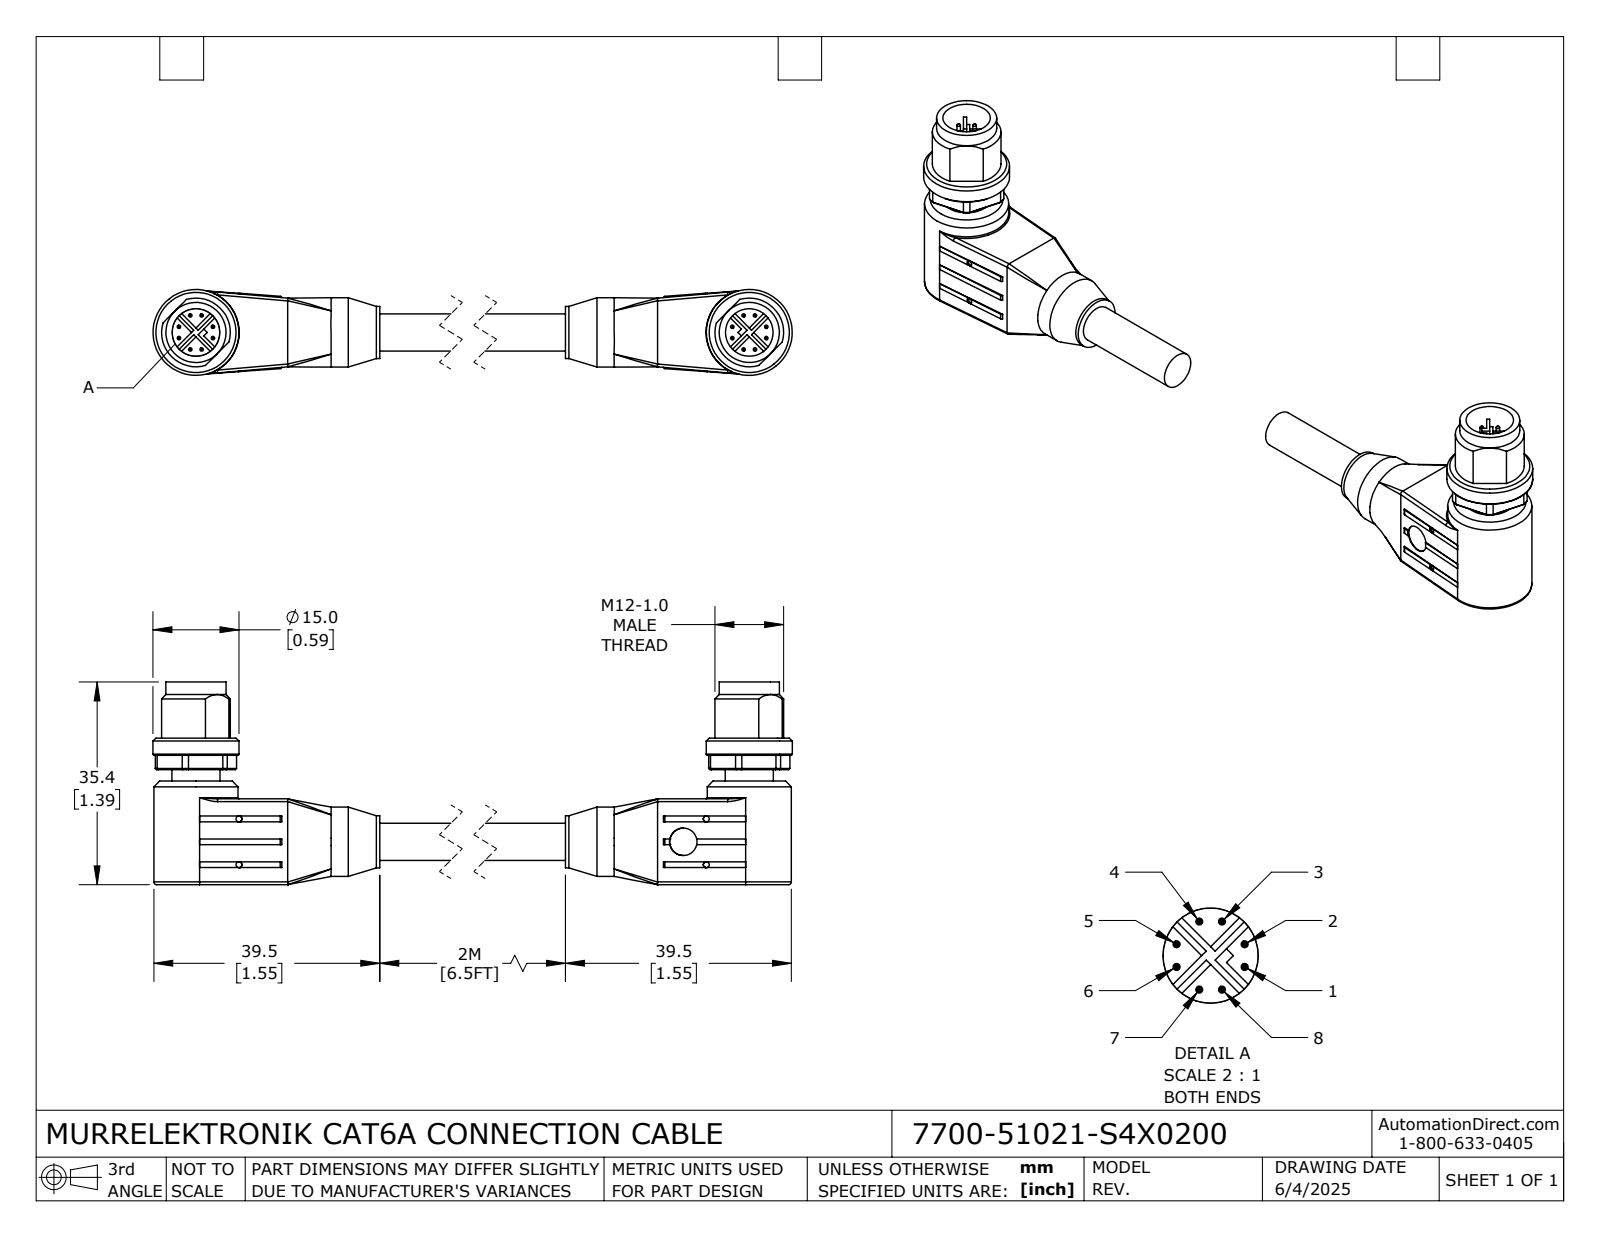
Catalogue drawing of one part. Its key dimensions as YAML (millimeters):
part_name: "7700-51021-S4X0200_MALE; 7700-51021-S4X0200"
step_written_by: "SolidWorks 2024 (CONFIG_CONTROL_DESIGN)"
units: millimeters
bodies: {solids: 2, faces: 424, planar: 196, cylindrical: 134, other: 94}
overall_size: [144.2, 35.4, 15]
volume: 18415
surface_area: 8016
round_holes:
  - {diameter: 1.05, count: 8}
  - {diameter: 4.8, count: 2}
  - {diameter: 8.3, count: 2}
round_bosses_or_shafts:
  - {diameter: 0.6, count: 16}
  - {diameter: 15, count: 2}
  - {diameter: 14.7, count: 2}
  - {diameter: 10.5, count: 2}
  - {diameter: 8.4, count: 2}
  - {diameter: 12.1, count: 1}
  - {diameter: 9.1, count: 1}
  - {diameter: 6.5, count: 1}
partial_cylinders:
  - {radius: 0.5, count: 8}
  - {radius: 0.3, count: 4}
  - {radius: 6, count: 2}
  - {radius: 7.2, count: 2}
face_to_face_distances: [3.59, 15, 91.34, 20.1, 5.1, 18.1, 3.1, 2, 1.1, 4.7]
hole_center_spacings: [8, 114.84, 115.12, 106.88, 129.2]
